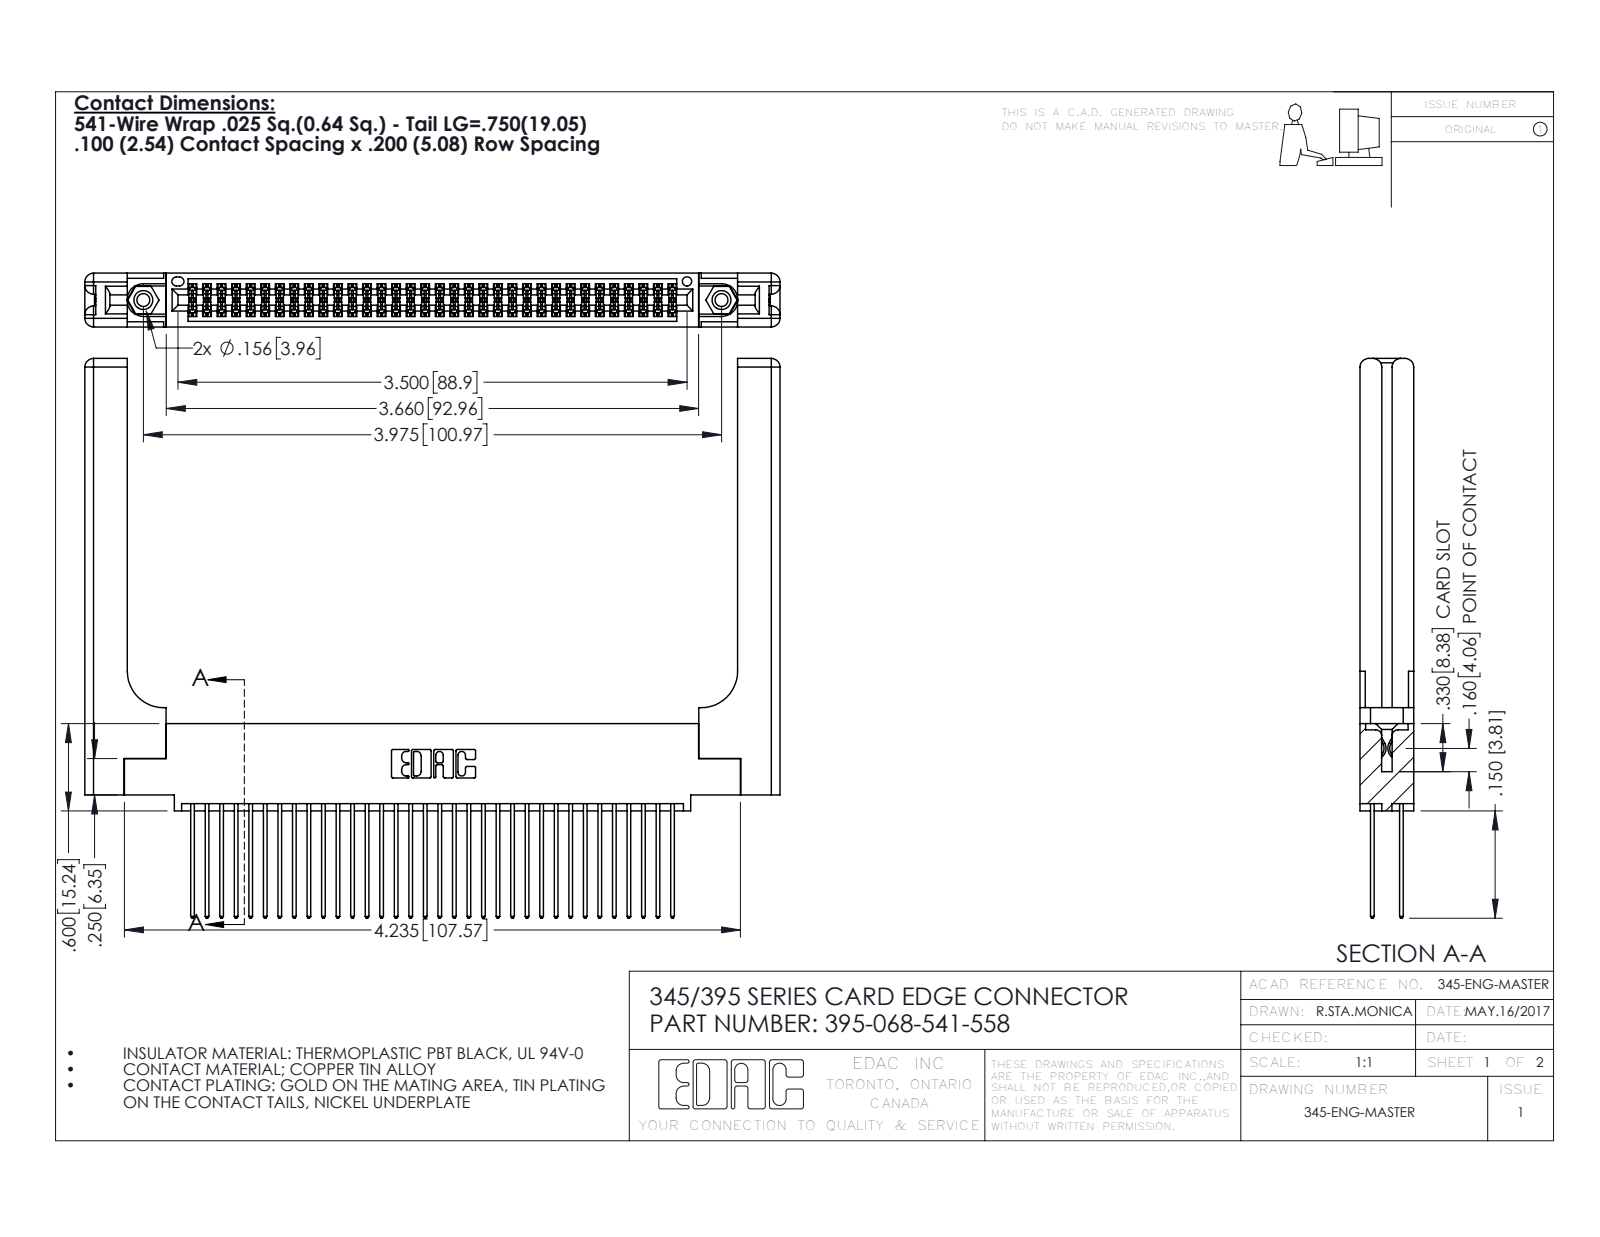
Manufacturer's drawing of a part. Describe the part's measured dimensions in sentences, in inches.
The part is named "345 Part_0.110 Offset - 0.156 Dia-TH; 345-292-001_345-293-141; 395-068-541-558; 345-250-001_345-250-001-102 (+1 more)". Its 3-D file was written by "SolidWorks 2016 (CONFIG_CONTROL_DESIGN)". It is 73 solids with 3786 faces: 2476 planar, 1250 cylindrical and 60 other. Overall it measures 4.779 by 3.847 by 0.37 inches. Its volume is 1.252 cubic inches and its surface area 38.16 square inches. Round holes: 2 of diameter 0.089, 2 of diameter 0.125, 2 of diameter 0.156, 1 of diameter 0.064. Round bosses or shafts: 2 of diameter 0.155. Partial cylindrical surfaces (rounded edges, fillets, slot ends): 102 of radius 0.006, 68 of radius 0.01, 22 of radius 0.01, 16 of radius 0.06, 6 of radius 0.007, 6 of radius 0.031, 3 of radius 0.026, 2 of radius 0.014. The main face-to-face distances are 0.072, 0.298, 0.37, 0.2, 0.098, 0.272, 0.025, 0.225, 0.175, 0.148. The hole center spacings are 0.27, 3.74, 3.975.
